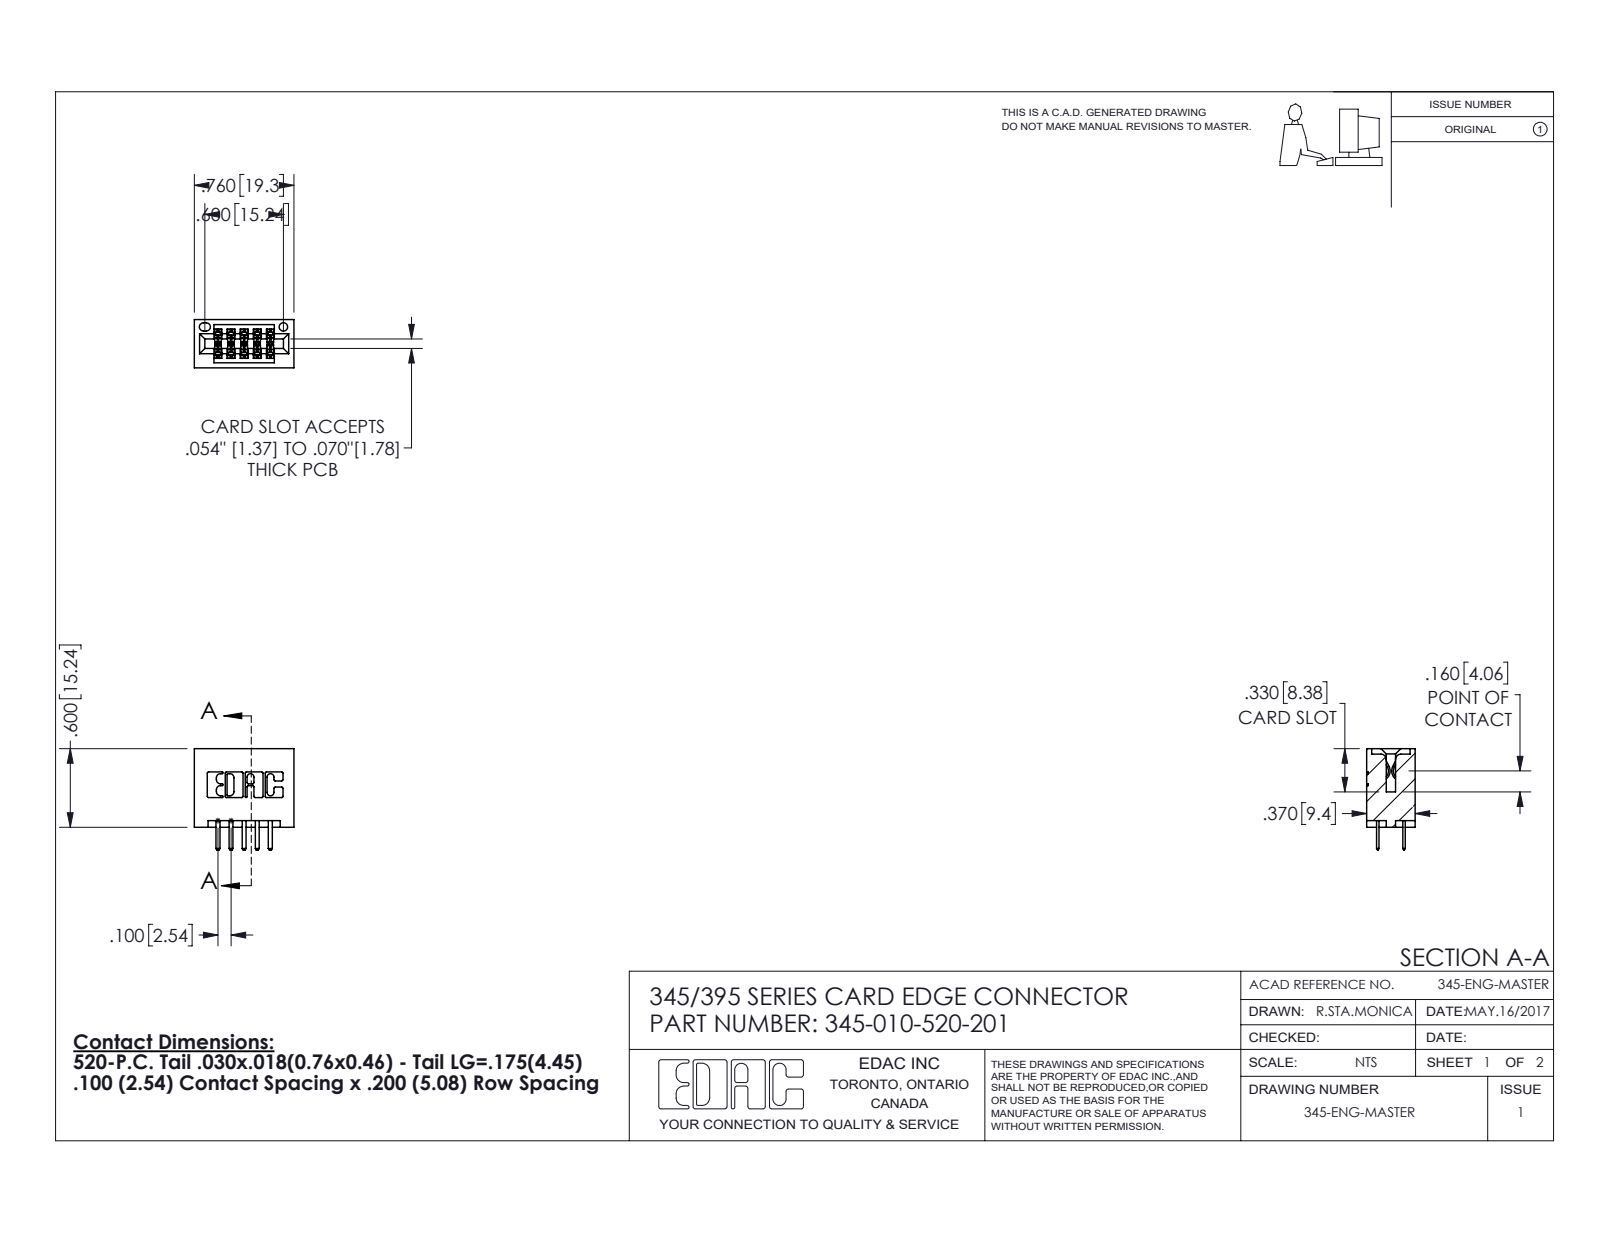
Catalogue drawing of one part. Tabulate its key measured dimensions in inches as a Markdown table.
| quantity | value |
| --- | --- |
| part name | 345-292-001_345-293-120; 345-010-520-201; 345 Part_No Mounting Lugs |
| STEP written by | SolidWorks 2016 (CONFIG_CONTROL_DESIGN) |
| units | inches |
| bodies | 11 solids, 658 faces (426 planar, 232 cylindrical, 0 other) |
| overall size | 0.775 × 0.76 × 0.37 |
| volume | 0.131 in³ |
| surface area | 4.255 in² |
| round holes (diameter × count) | 0.064 × 1 |
| partial cylindrical surfaces (radius × count) | 0.01 × 22, 0.006 × 15, 0.01 × 14, 0.007 × 6, 0.031 × 6, 0.026 × 3, 0.014 × 2, 0.019 × 2 |
| main face-to-face distances | 0.2, 0.298, 0.072, 0.1, 0.37, 0.098, 0.272, 0.025, 0.06, 0.225 |
